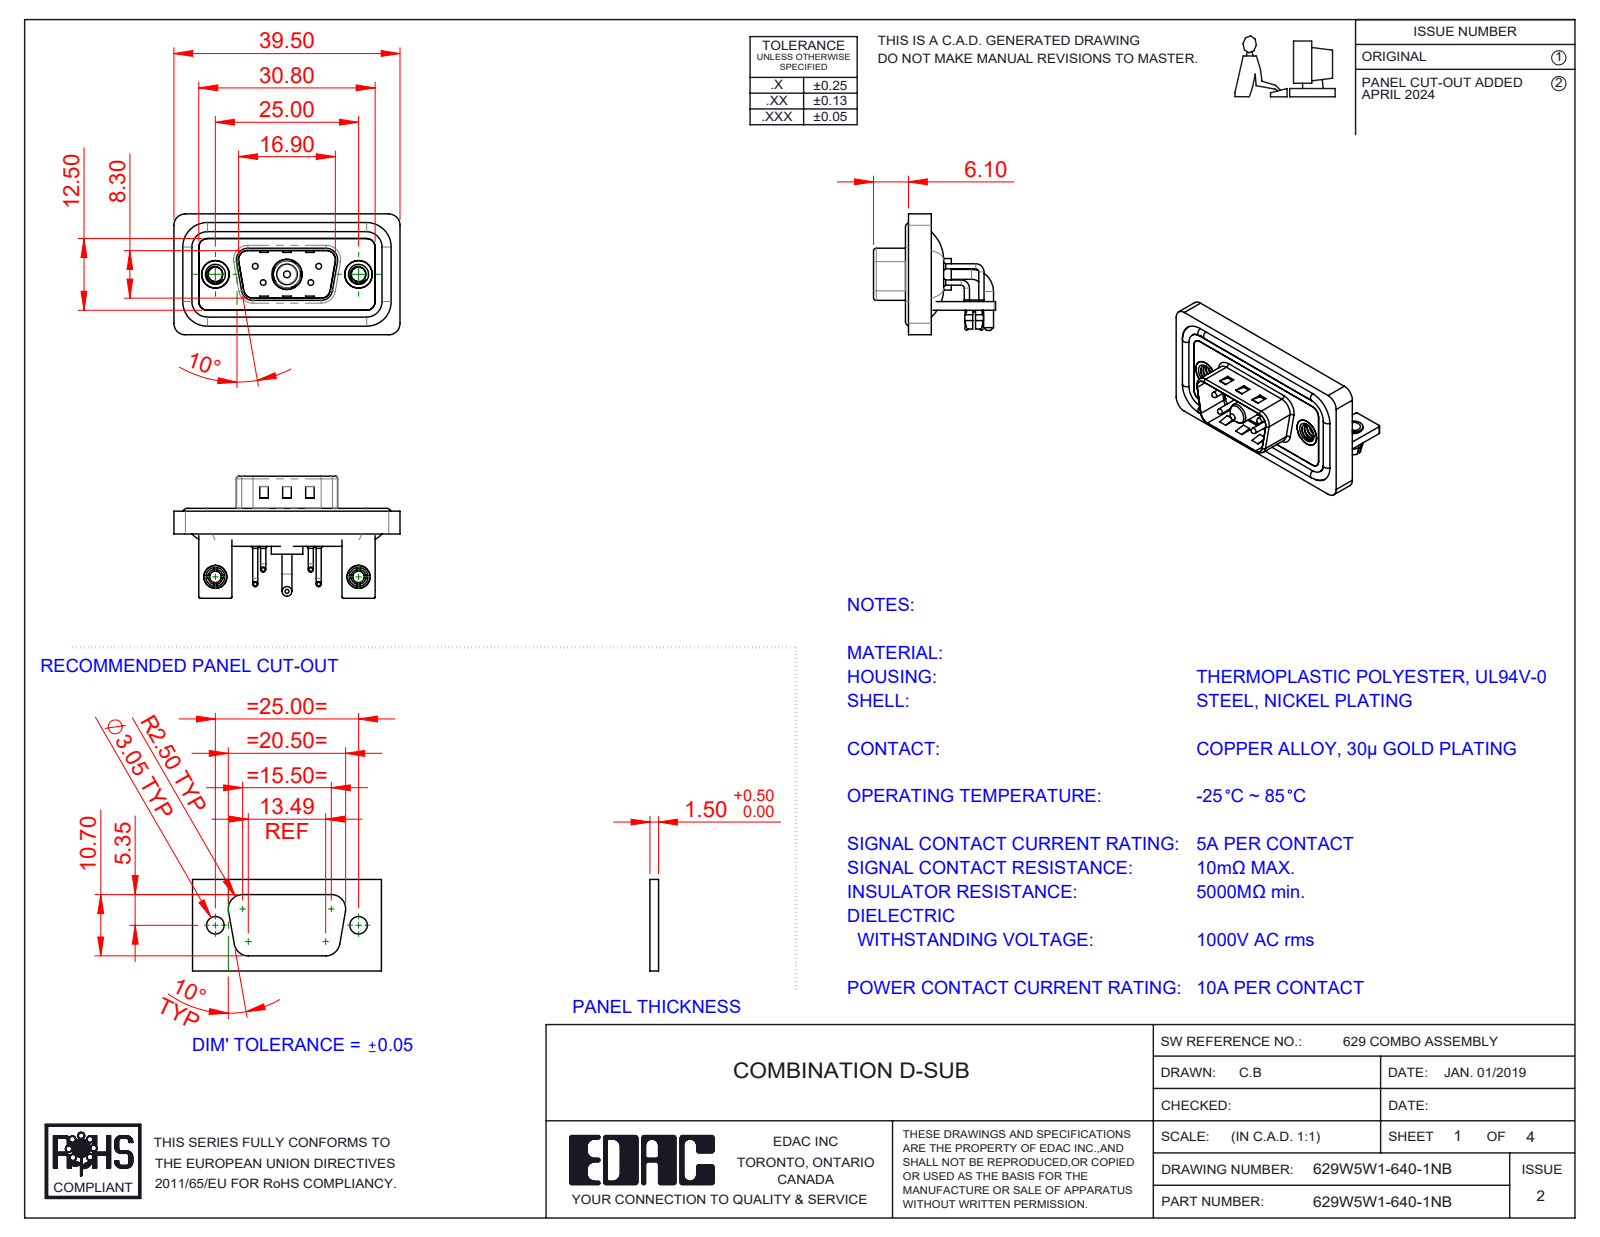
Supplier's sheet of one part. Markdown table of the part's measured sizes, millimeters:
| quantity | value |
| --- | --- |
| part name | Power Pin_10A RA; 629Combo Contact Row 1; 629Combo Housing_5W1; 629Combo Contact Row 2 (+7 more) |
| STEP written by | SolidWorks 2023 (CONFIG_CONTROL_DESIGN) |
| units | millimeters |
| bodies | 17 solids, 1024 faces (479 planar, 395 cylindrical, 150 other) |
| overall size | 39.5 × 21.3 × 21.1 |
| volume | 4 726 mm³ |
| surface area | 7 911 mm² |
| round holes (diameter × count) | 2 × 6, 0.75 × 4, 1.6 × 4, 2.5 × 4, 3.2 × 2, 4 × 2, 4.8 × 2, 5 × 2, 4.85 × 1, 5.3 × 1 |
| round bosses / shafts (diameter × count) | 0.9 × 8, 1.6 × 4, 1.5 × 4, 1 × 4, 0.65 × 4, 4.9 × 2, 4 × 2, 3.4 × 2 |
| partial cylindrical surfaces (radius × count) | 2 × 19, 1.5 × 18, 0.25 × 16, 0.5 × 9, 1.6 × 8, 0.6 × 4, 0.65 × 4, 0.9 × 4 |
| main face-to-face distances | 0.4, 1.5, 0.8, 2.9, 1.1, 2.1, 1.2, 1.6, 2.5, 3.7 |
| hole center spacings | 3.16, 5.72, 7.1, 12.5, 18.1, 25, 4.39, 4.4 |
